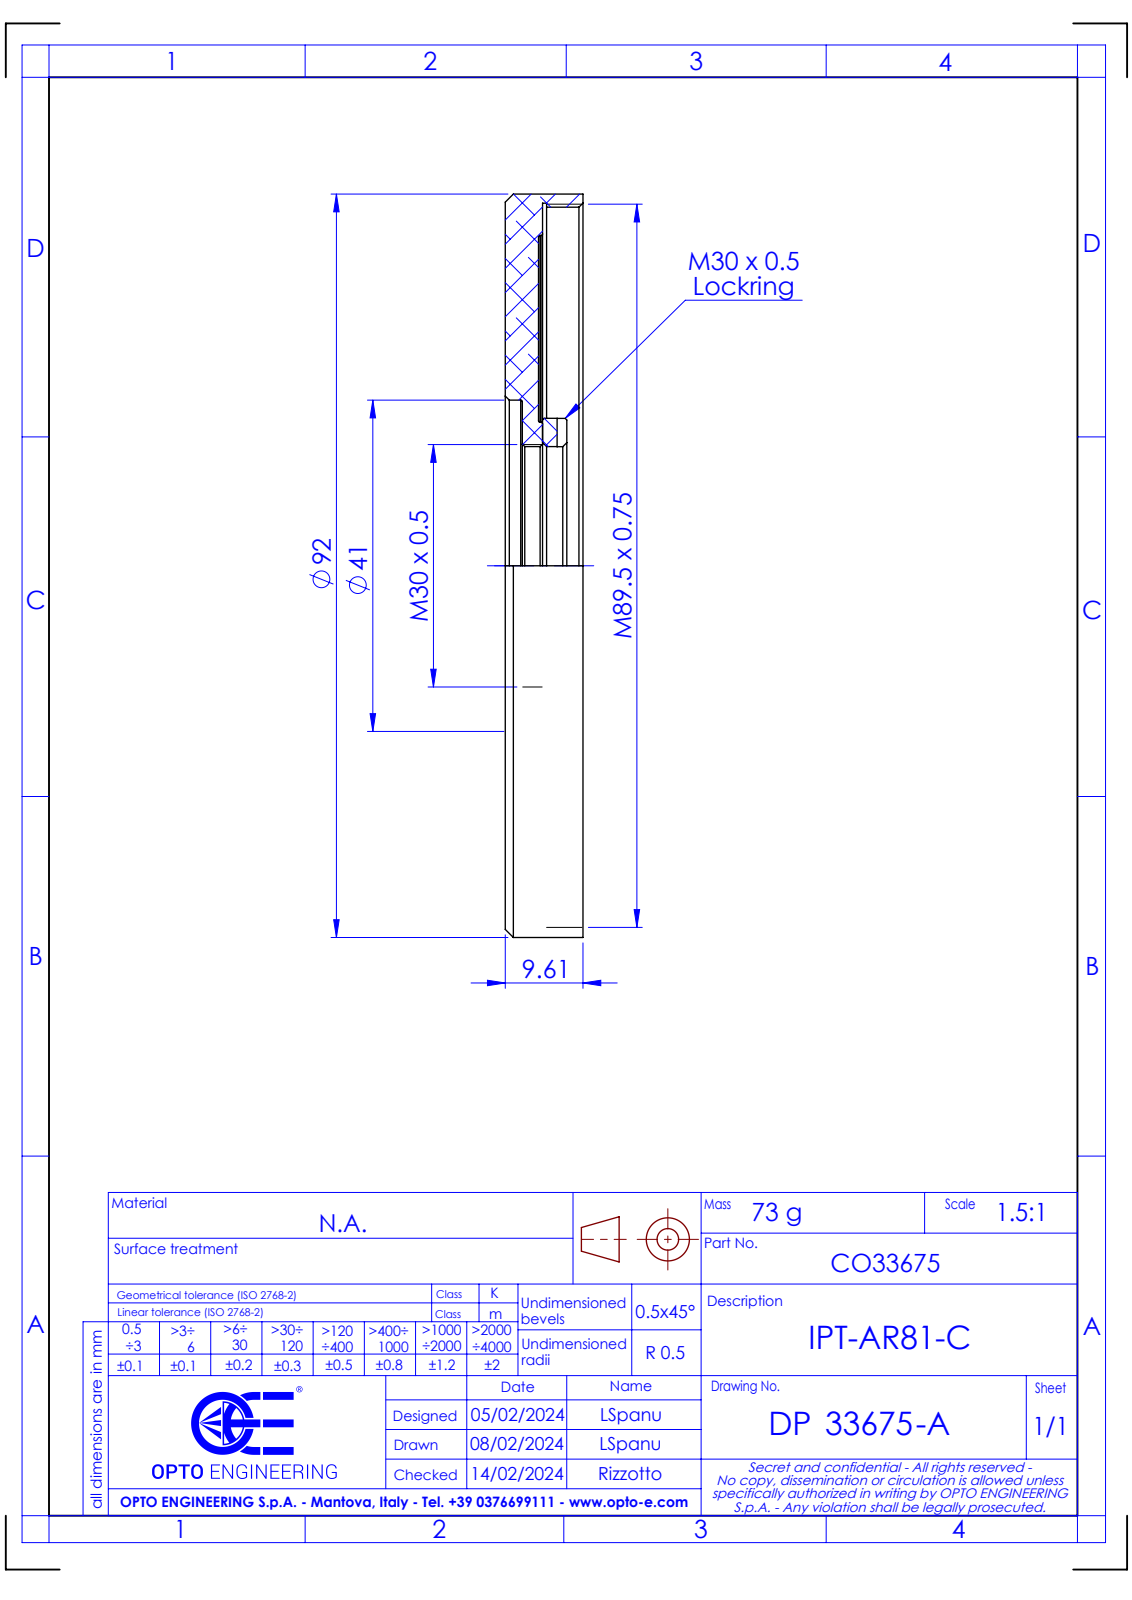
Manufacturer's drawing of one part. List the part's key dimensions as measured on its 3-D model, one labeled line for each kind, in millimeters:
Part name (STEP PRODUCT): DP33675-A_IPT-AR81-C
STEP written by: SolidWorks 2021 (CONFIG_CONTROL_DESIGN)
Units: millimetres
Bodies: 0 solids, 58 faces (14 planar, 18 cylindrical, 26 other)
Overall size (bounding box): 92 × 92 × 9.61
Round holes (diameter × count): ⌀29.5 ×1, ⌀41 ×1, ⌀81.75 ×1, ⌀88.75 ×1, ⌀89.75 ×1
Round bosses / shafts (diameter × count): ⌀92 ×1, ⌀36.5 ×1, ⌀35.5 ×1
Main face-to-face distances: 4.11, 4.61, 0.5, 2, 5.5, 2.11, 2.5, 9.61, 7.5, 5
